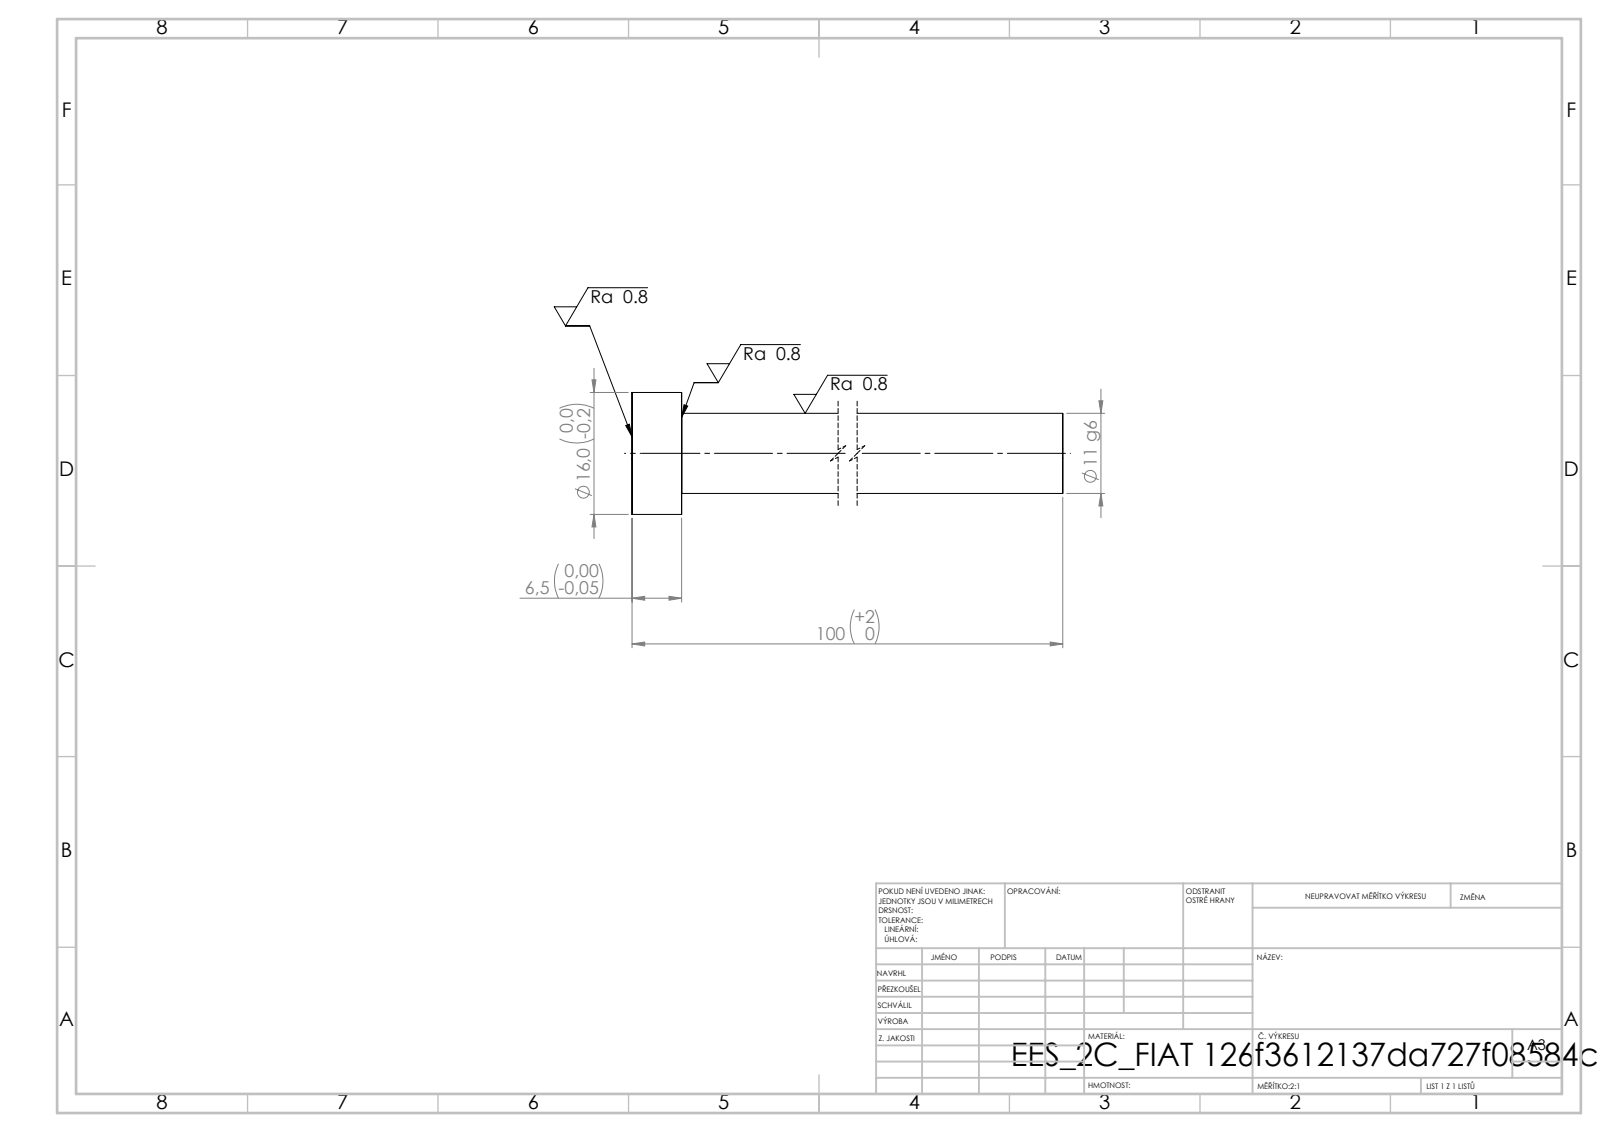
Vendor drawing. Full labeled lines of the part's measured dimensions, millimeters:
STEP written by: SolidWorks 2019 (CONFIG_CONTROL_DESIGN)
Units: millimetres
Bodies: 1 solid, 7 faces (3 planar, 4 cylindrical, 0 other)
Overall size (bounding box): 100 × 16 × 16
Volume: 9 403 mm³ · Surface area: 3 813 mm²
Round bosses / shafts (diameter × count): ⌀16 ×1, ⌀10.5 ×1
Main face-to-face distances: 6.5, 100, 93.5
